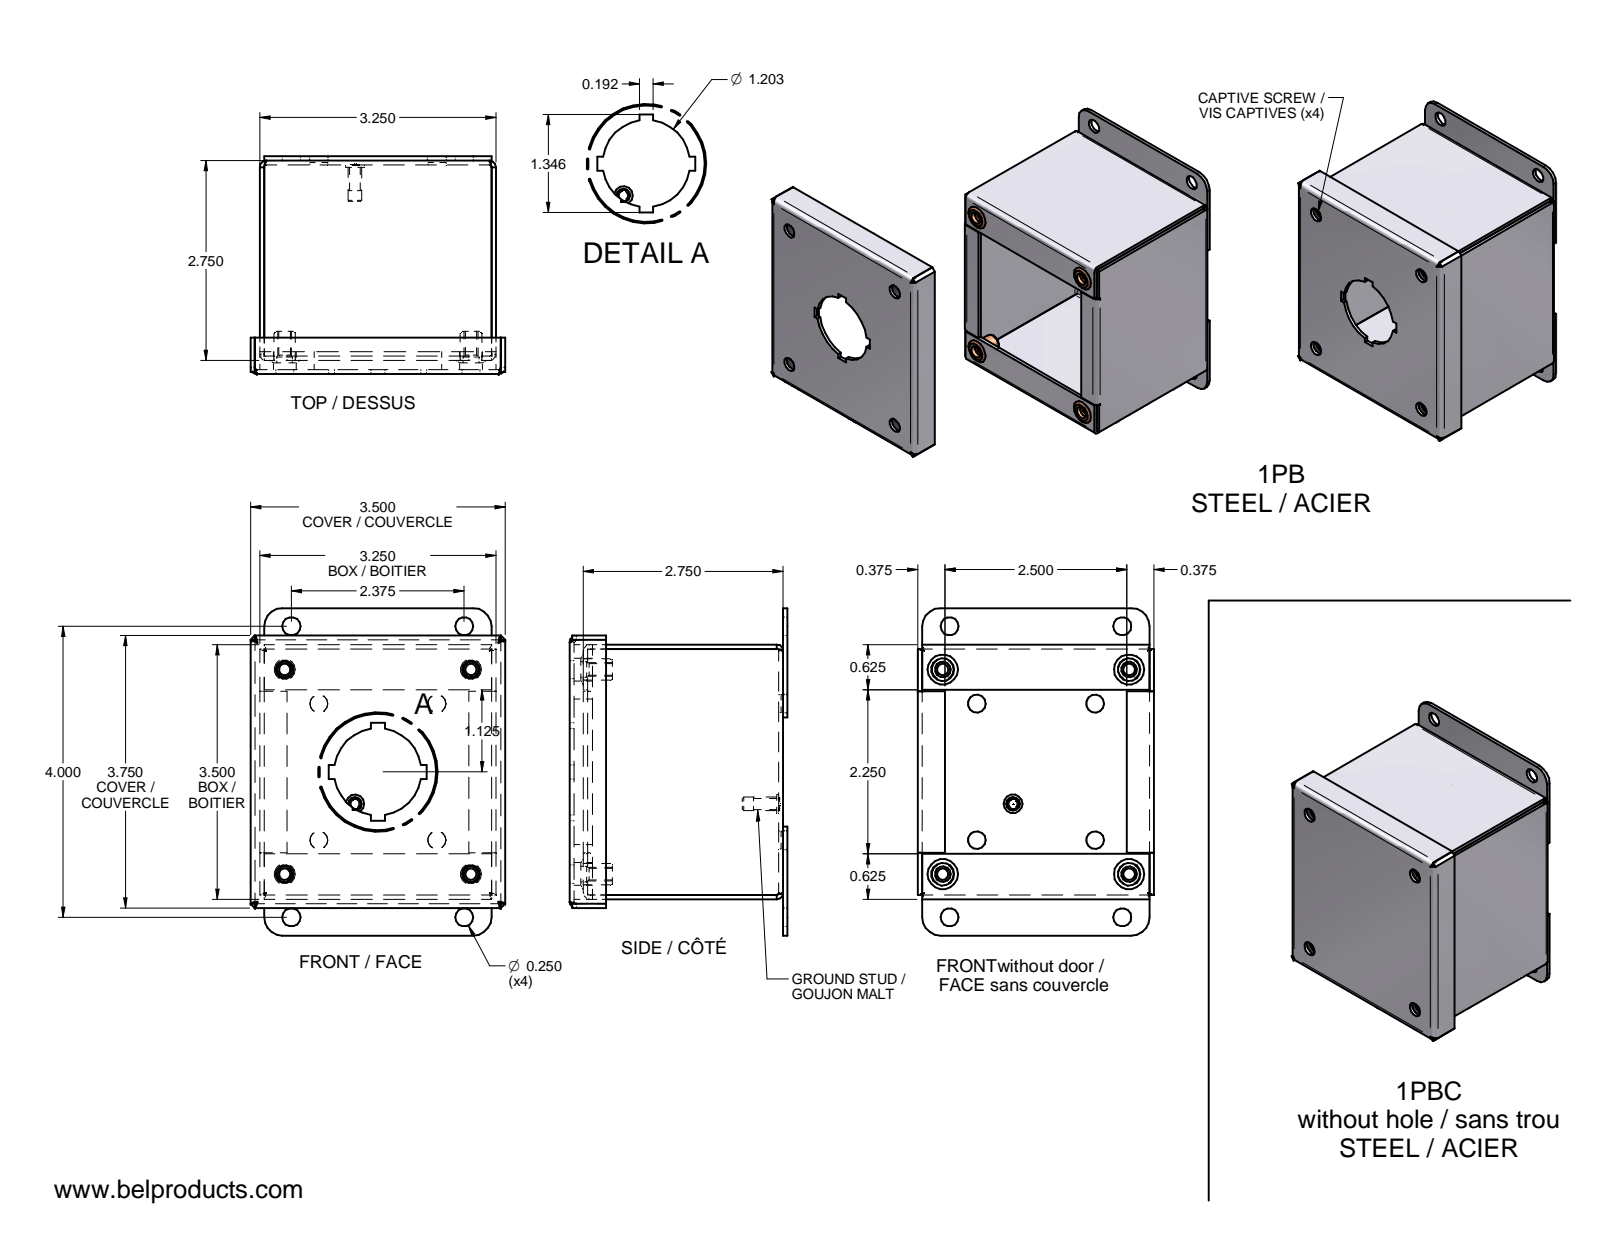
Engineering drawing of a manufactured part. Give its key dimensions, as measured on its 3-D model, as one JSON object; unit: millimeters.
{"part_name": "1PB_BOITIER; 1PB-B; INSERT 10-32 AVK ALS4-1032-130; 1PB-P (+4 more)", "step_written_by": "Unknown (AUTOMOTIVE_DESIGN)", "units": "millimeters", "bodies": {"solids": 10, "faces": 335, "planar": 205, "cylindrical": 73, "other": 57}, "overall_size": [114.3, 88.9, 76.07], "volume_mm3": 110180, "surface_area_mm2": 121509, "round_holes": [[6.35, 8], [4.04, 4], [5.49, 4], [6.22, 4], [6.73, 4], [7.37, 4], [7.92, 4], [3.17, 1]], "round_bosses_or_shafts": [[7.52, 4], [6.35, 4], [6.5, 1], [4.83, 1], [3.02, 1], [0.51, 1]], "partial_cylinders_radius": [[0.81, 12], [2.34, 12], [6.35, 4]], "face_to_face_distances": [1.52, 73.03, 74.55, 87.38, 81.02, 4.7, 3.18, 3.17, 88.9, 69.85], "hole_center_spacings": [15.28, 15.29, 16.79, 16.83, 28.62, 54.46, 54.5, 57.52]}
